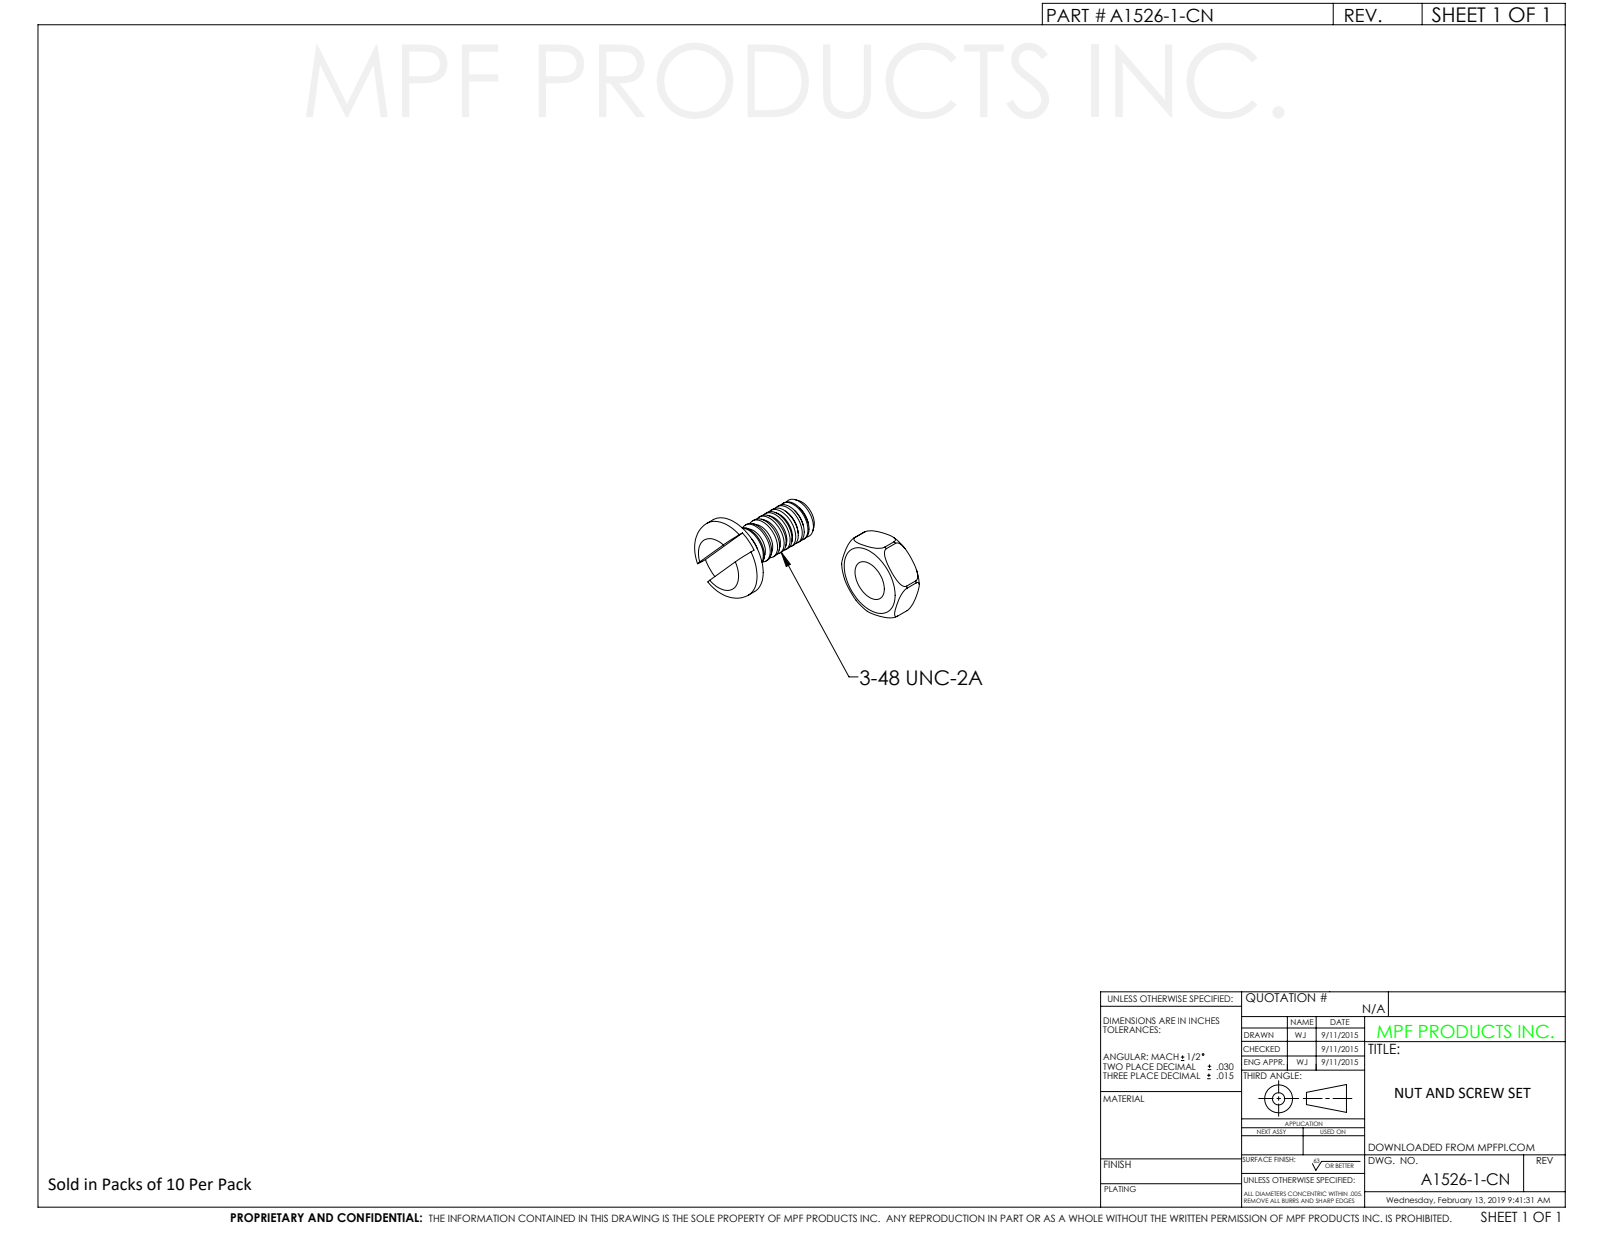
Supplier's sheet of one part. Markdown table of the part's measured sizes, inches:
| quantity | value |
| --- | --- |
| part name | A1526-1-CN |
| STEP written by | SolidWorks 2012 (CONFIG_CONTROL_DESIGN) |
| units | inches |
| bodies | 2 solids, 94 faces (15 planar, 30 cylindrical, 49 other) |
| overall size | 0.486 × 0.27 × 0.197 |
| volume | 0.004 in³ |
| surface area | 0.269 in² |
| round holes (diameter × count) | 0.095 × 1 |
| round bosses / shafts (diameter × count) | 0.19 × 1, 0.095 × 1 |
| partial cylindrical surfaces (radius × count) | 0.102 × 1 |
| main face-to-face distances | 0.22, 0.18, 0.07, 0.15, 0.23, 0.16, 0.27, 0.2, 0.05, 0.04 |
